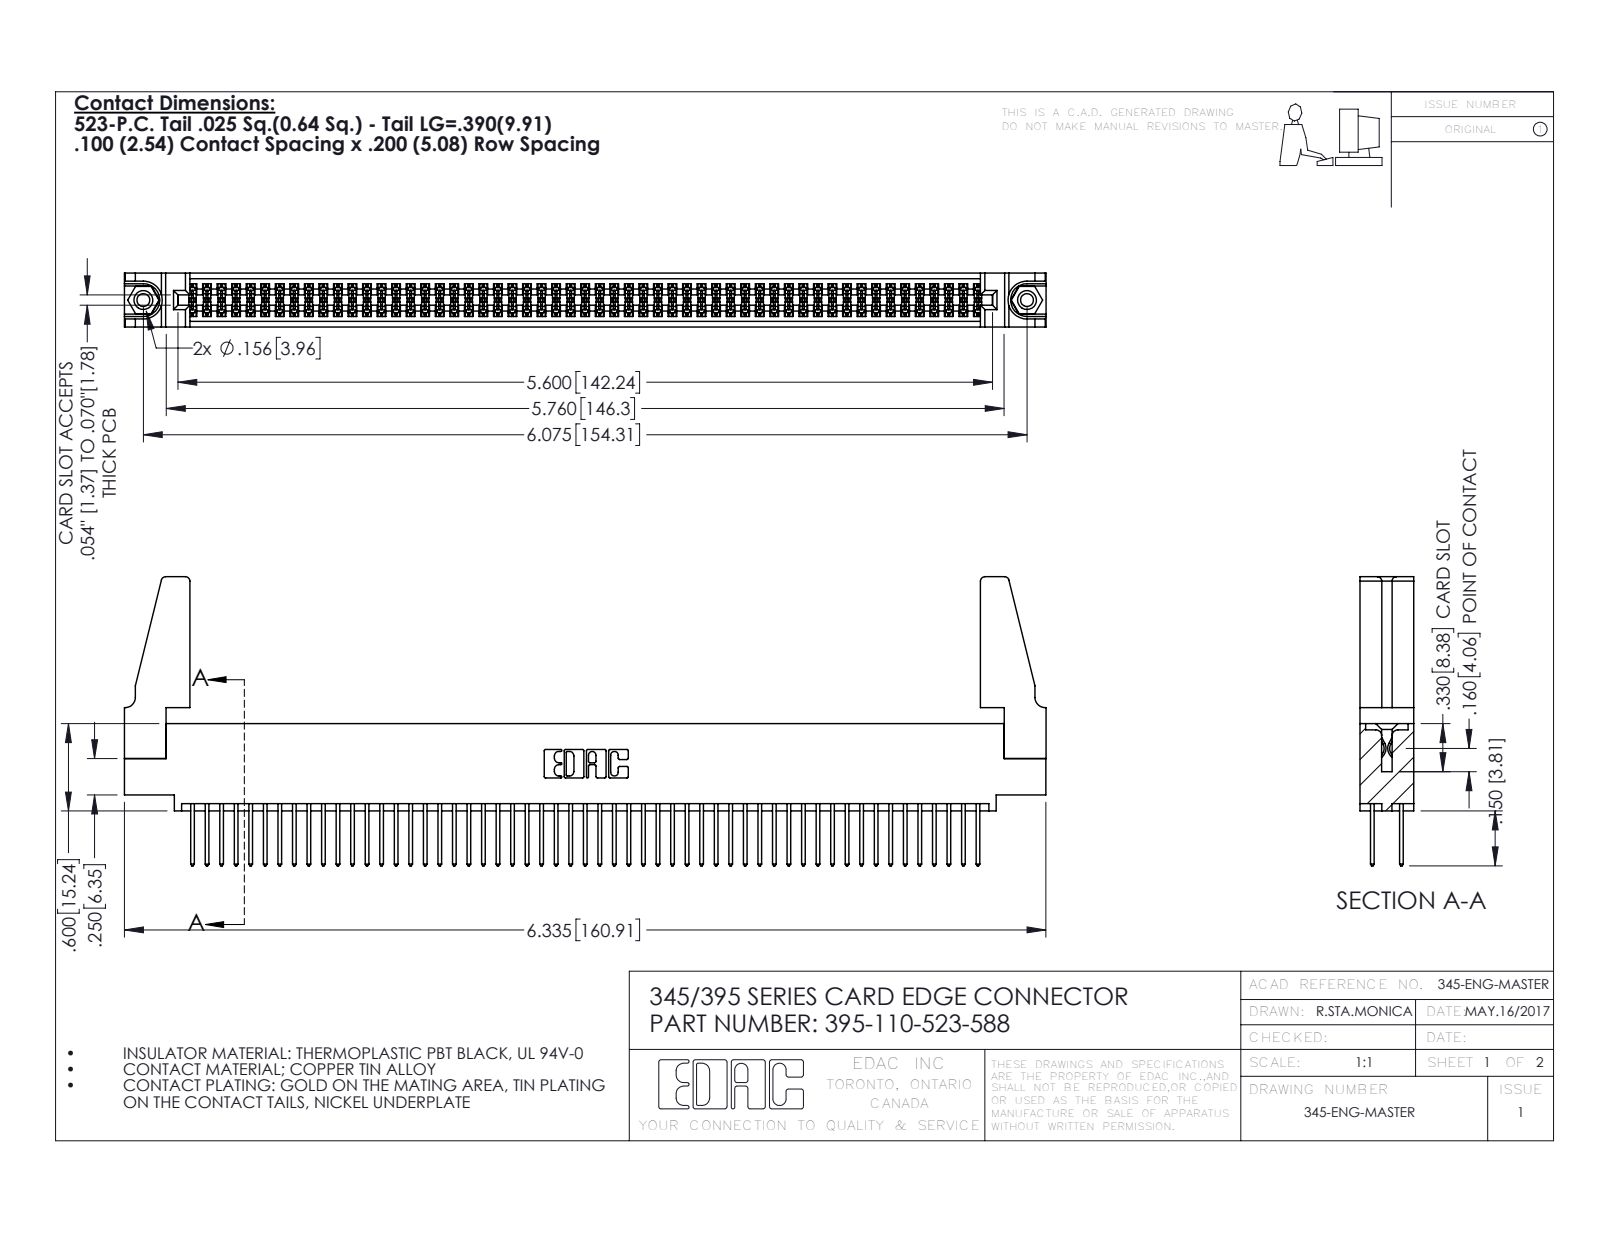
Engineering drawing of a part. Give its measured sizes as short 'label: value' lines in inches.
name: 345-220-078_345-220-088; 345-292-001_345-293-123; 345-250-001_345-250-001-102; 395-110-523-588 (+1 more)
written by: SolidWorks 2016 (CONFIG_CONTROL_DESIGN)
unit: in
bodies: 115 solids, 5754 faces (3786 planar, 1952 cylindrical, 16 other)
size: 6.336 × 1.987 × 0.37
volume: 1.169 in³; area: 43.38 in²
holes: 2× ⌀0.089, 2× ⌀0.125, 2× ⌀0.156, 1× ⌀0.064
bosses: 2× ⌀0.155
rounds: 165× R0.006, 110× R0.01, 22× R0.01, 8× R0.03, 6× R0.007, 6× R0.031, 3× R0.026, 2× R0.014
face distances: 0.072, 0.298, 0.37, 0.2, 0.098, 0.272, 0.025, 0.225, 0.175, 0.149
hole spacings: 0.27, 5.839, 6.075
